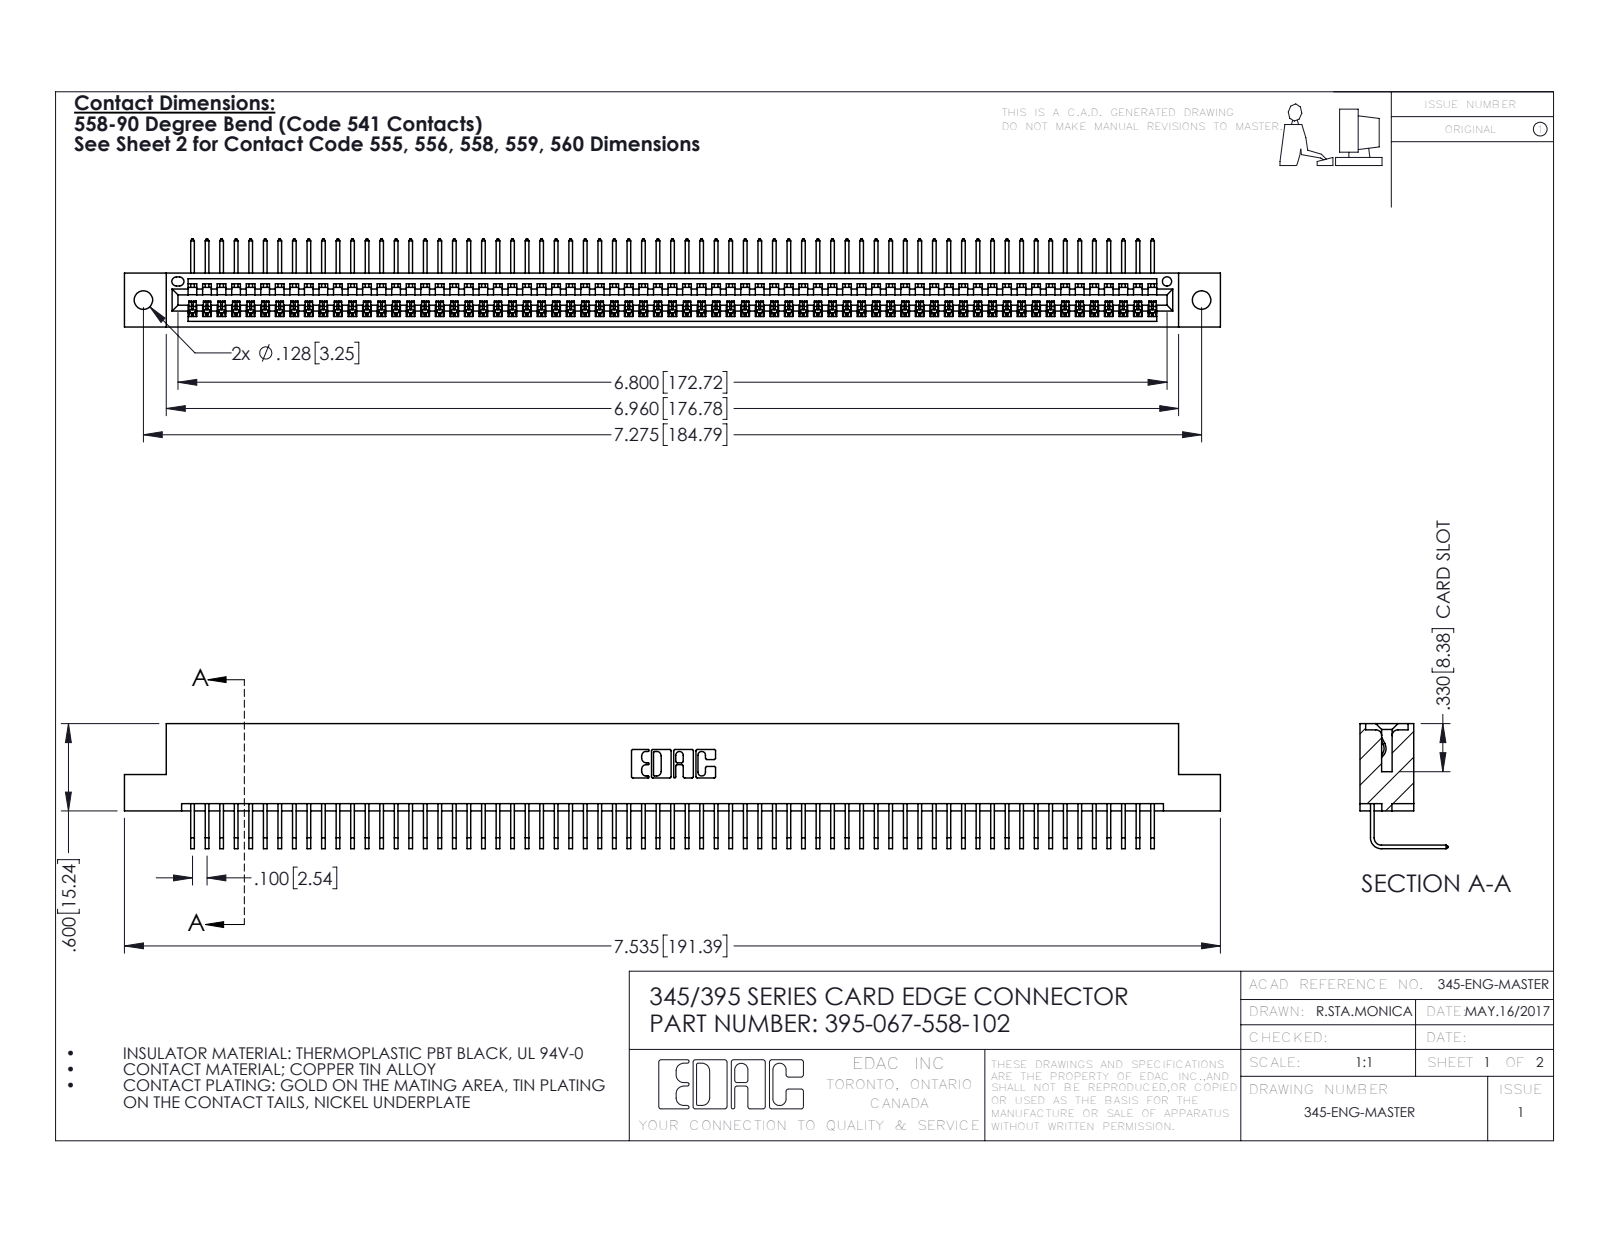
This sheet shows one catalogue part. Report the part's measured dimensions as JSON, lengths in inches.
{"part_name": "395-067-558-102; 345 Part_Flush Mounting Lugs - 0.128 Dia; 345-292-001_558 Tail - 2", "step_written_by": "SolidWorks 2016 (CONFIG_CONTROL_DESIGN)", "units": "inches", "bodies": {"solids": 68, "faces": 4146, "planar": 2894, "cylindrical": 1252, "other": 0}, "overall_size": [7.535, 0.859, 0.605], "volume_in3": 1.133, "surface_area_in2": 40.39, "round_holes": [[0.128, 2], [0.064, 1]], "partial_cylinders_radius": [[0.006, 134], [0.01, 22], [0.007, 6], [0.031, 6], [0.026, 3], [0.031, 2], [0.04, 2], [0.014, 1]], "face_to_face_distances": [0.298, 0.072, 0.37, 0.2, 0.098, 0.272, 0.025, 0.225, 0.149, 0.072], "hole_center_spacings": [0.27, 7.039, 7.275]}
